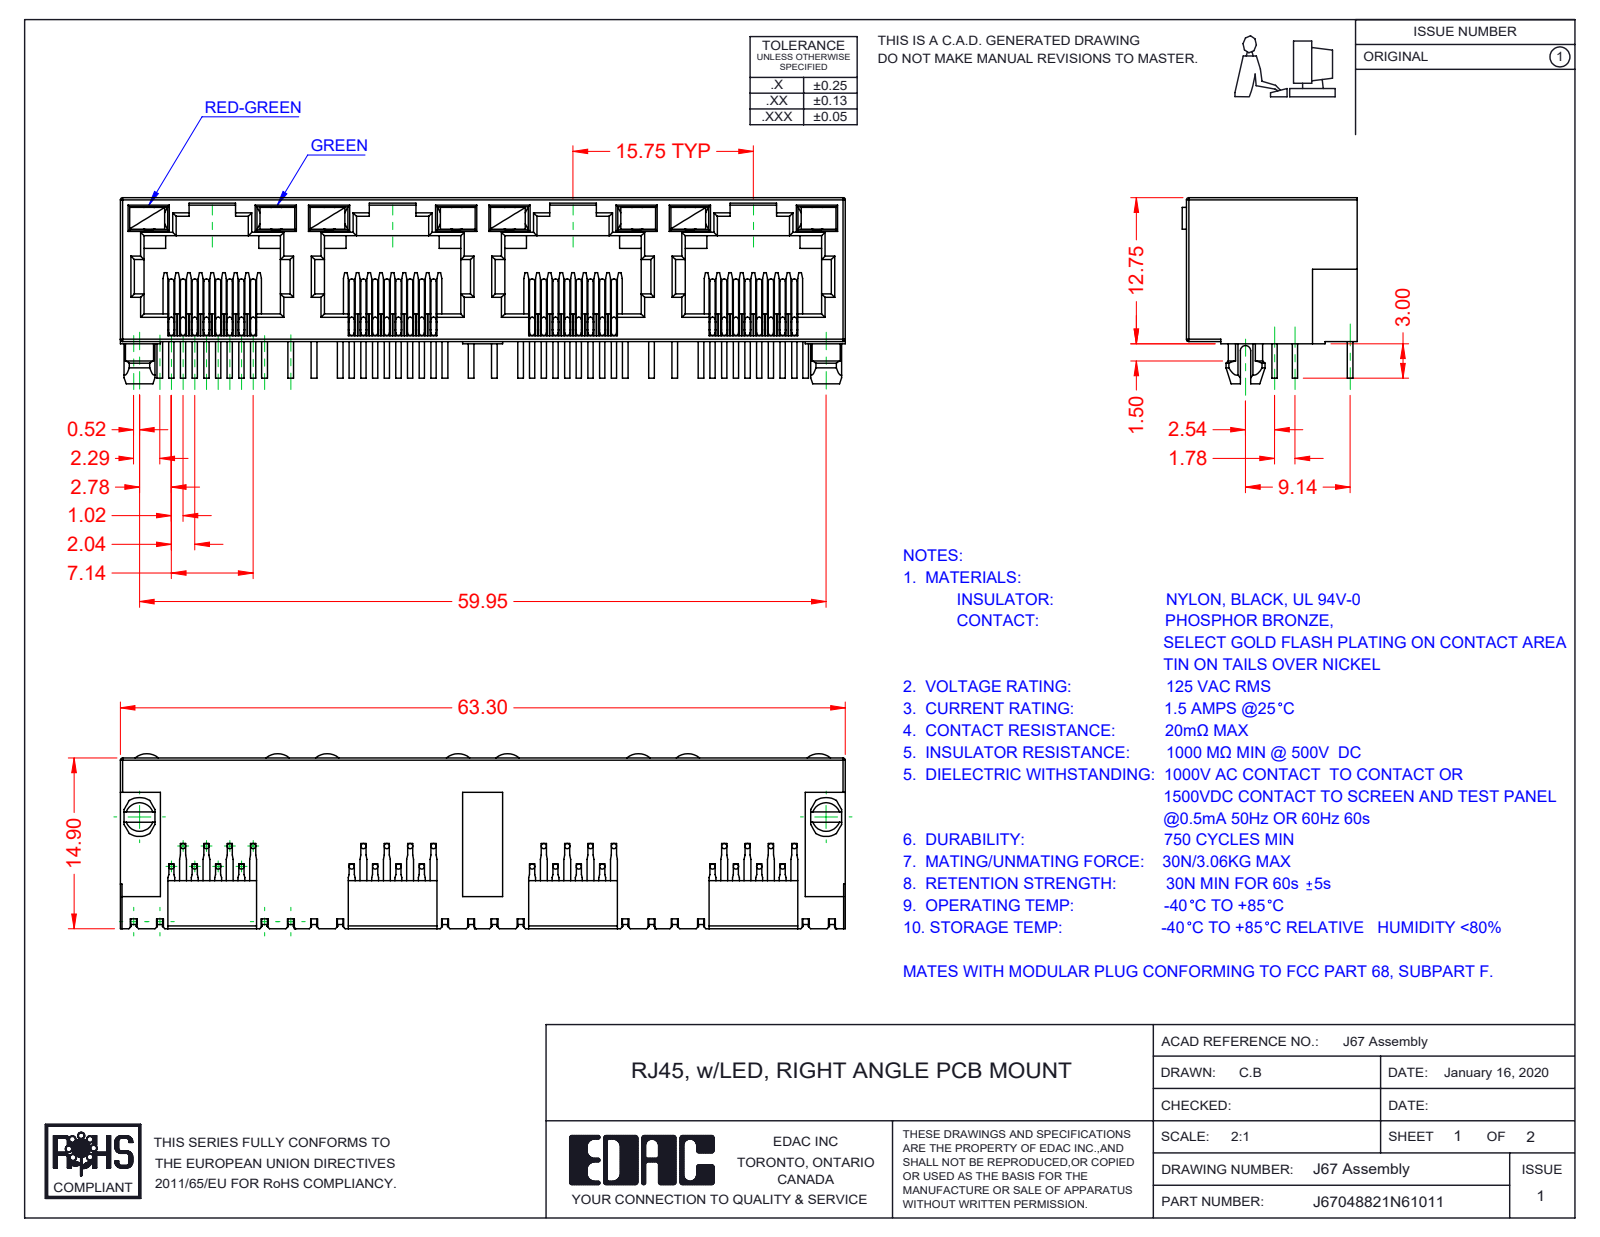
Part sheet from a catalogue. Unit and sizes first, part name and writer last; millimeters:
Units: millimetres
Overall size (bounding box): 63.3 × 16.25 × 15.28
Round bosses / shafts (diameter × count): ⌀0.46 ×96
Partial cylindrical surfaces — rounded edges, fillets, slot ends (radius × count): R0.2 ×66, R0.3 ×29, R0.45 ×9, R1.55 ×8, R1.5 ×2, R1.7 ×2, R0.35 ×1, R1 ×1
Main face-to-face distances: 0.5, 12.55, 1.89, 0.89, 10, 15.75, 1, 1.39, 11, 11.89
Volume: 5 159 mm³ · Surface area: 11 573 mm²
Bodies: 41 solids, 2473 faces (1781 planar, 484 cylindrical, 208 other)
Part name (STEP PRODUCT): 67 LED RH_3-Green; 67 Contacts; 67 Insulator; J67048822N63011 (+1 more)
STEP written by: SolidWorks 2016 (CONFIG_CONTROL_DESIGN)
